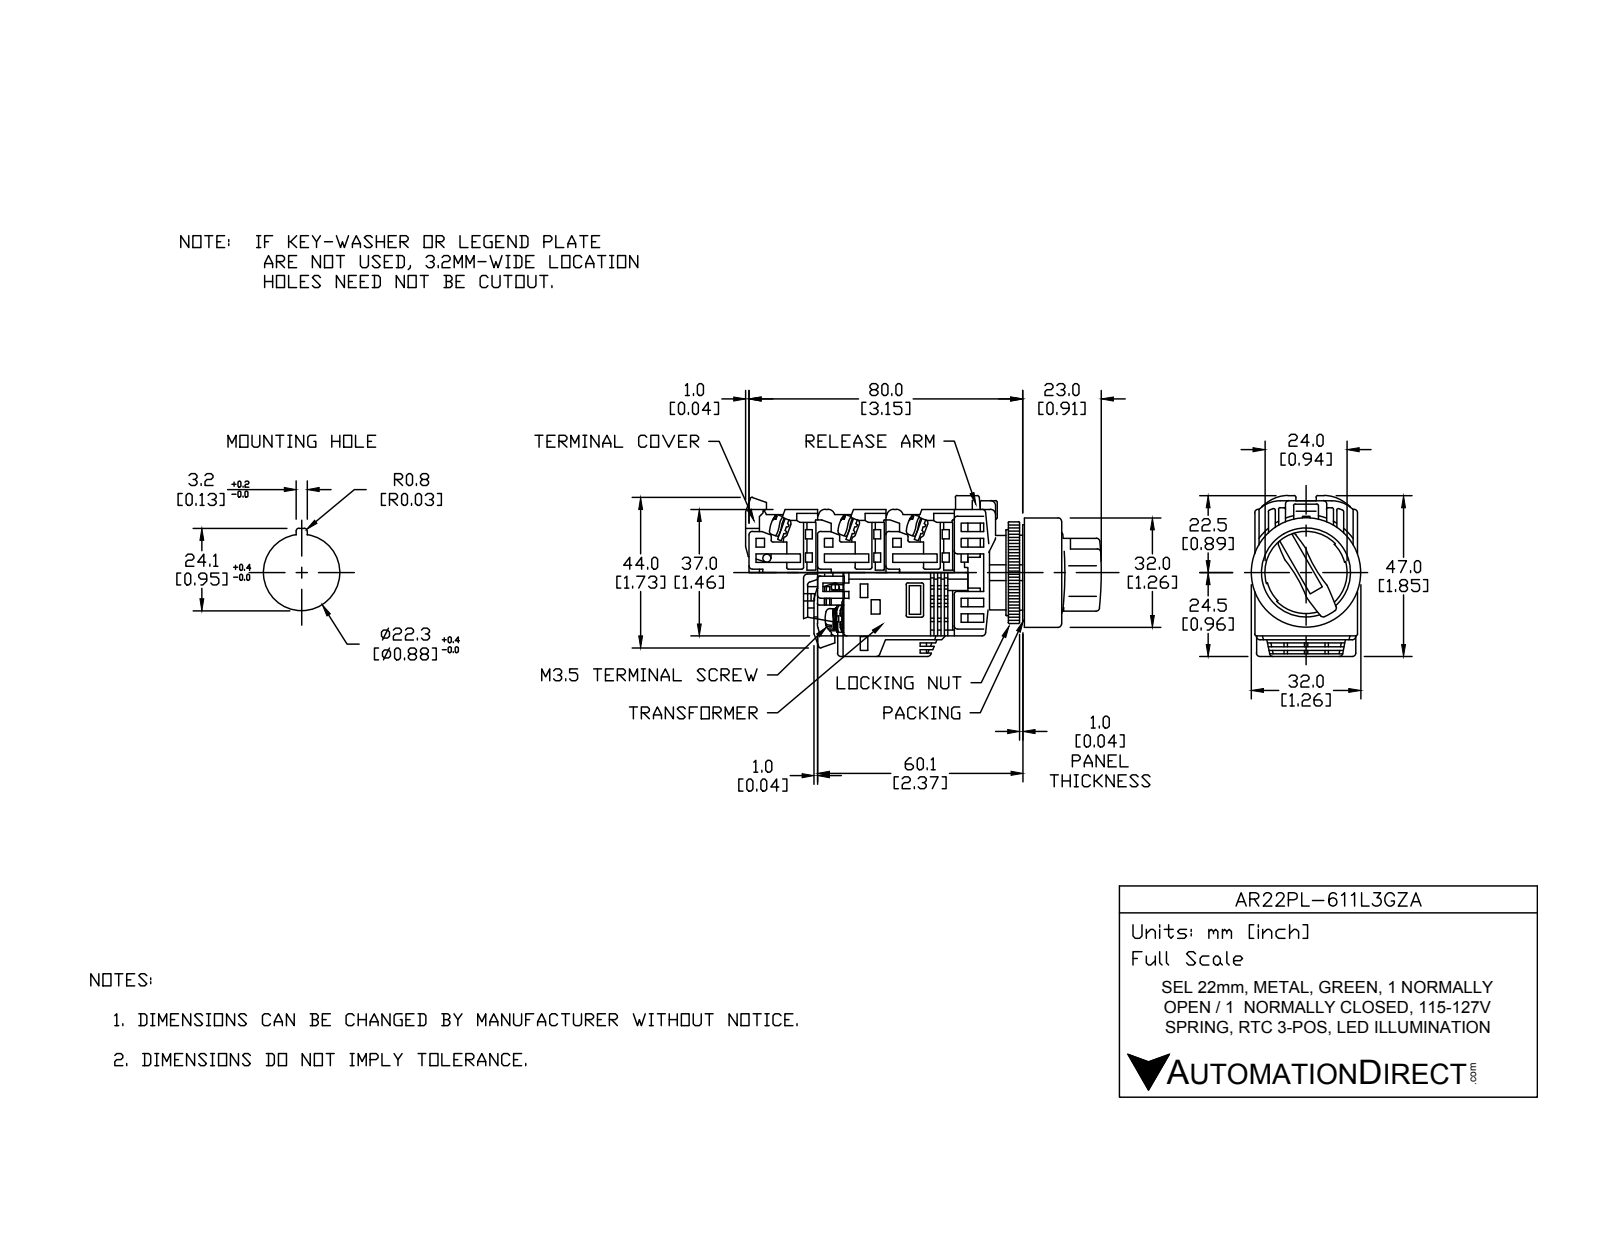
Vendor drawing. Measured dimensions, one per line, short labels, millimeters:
name: AR22PL-611L3GZA
written by: SolidWorks 2017 (AUTOMOTIVE_DESIGN)
unit: mm
bodies: 23 solids, 556 faces (386 planar, 139 cylindrical, 31 other)
size: 84.5 × 43.81 × 32
volume: 57 503 mm³; area: 30 219 mm²
holes: 1× ⌀21.8, 1× ⌀22, 1× ⌀25, 1× ⌀31
bosses: 6× ⌀5, 1× ⌀32, 1× ⌀30.5, 1× ⌀29.8, 1× ⌀24, 1× ⌀21.75, 1× ⌀17
rounds: 48× R0.5, 8× R1.75, 6× R1, 4× R5, 2× R4, 1× R12, 1× R16.59, 1× R17.59
face distances: 1, 18, 20, 29, 3, 40, 28.5, 68.5, 2, 10
